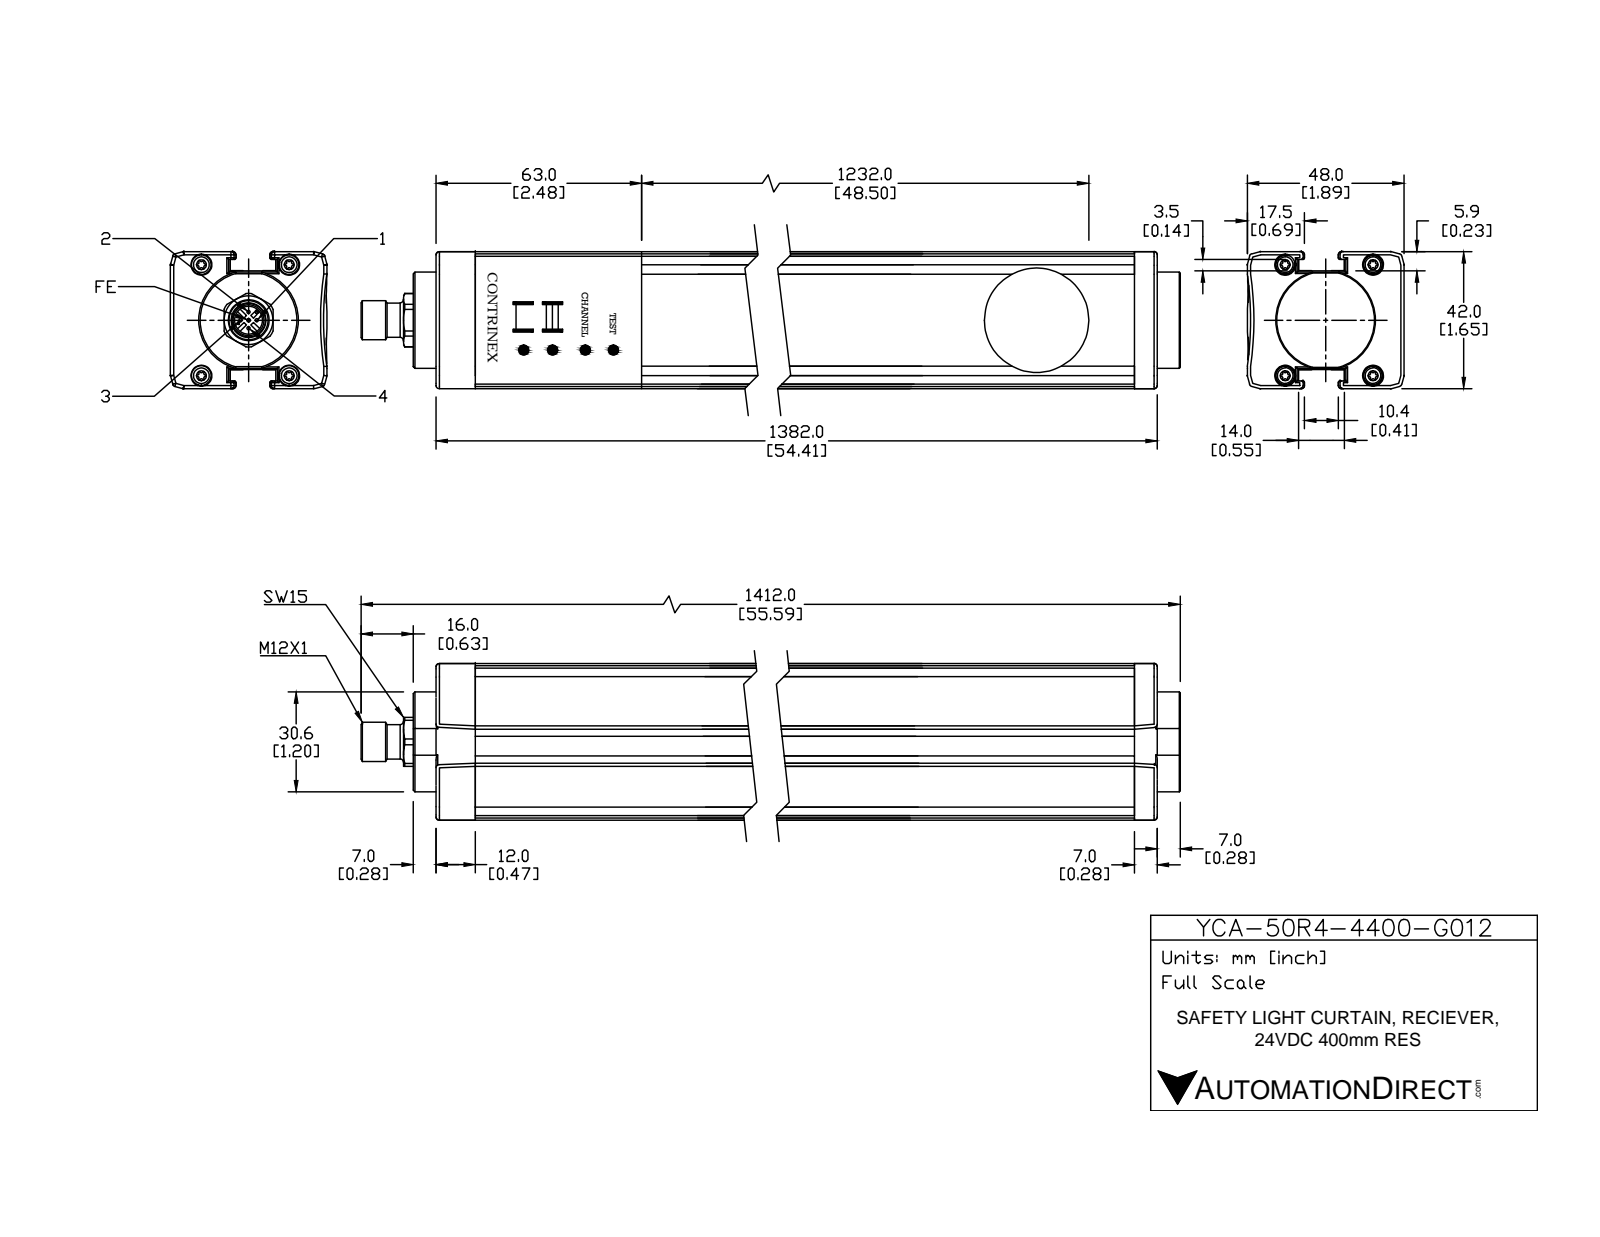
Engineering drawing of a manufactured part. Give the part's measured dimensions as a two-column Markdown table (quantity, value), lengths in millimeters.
| quantity | value |
| --- | --- |
| part name | YCA-50R4-4400-G012 |
| STEP written by | SolidWorks 2016 (AUTOMOTIVE_DESIGN) |
| units | millimeters |
| bodies | 18 solids, 454 faces (221 planar, 172 cylindrical, 61 other) |
| overall size | 1412 × 48 × 42 |
| volume | 2 487 000 mm³ |
| surface area | 315 052 mm² |
| round holes (diameter × count) | 6 × 4, 1 × 1, 8.5 × 1, 32 × 1 |
| round bosses / shafts (diameter × count) | 5.5 × 4, 1 × 4, 30.6 × 1, 12 × 1, 10.5 × 1 |
| partial cylindrical surfaces (radius × count) | 1 × 52, 0.5 × 4, 8.2 × 1, 100 × 1 |
| main face-to-face distances | 42, 5.8, 36.2, 29.4, 1, 6.8, 35.2, 30.4, 14, 17.2 |
| hole center spacings | 21.04, 22.34, 26.9, 34, 43.35 |
